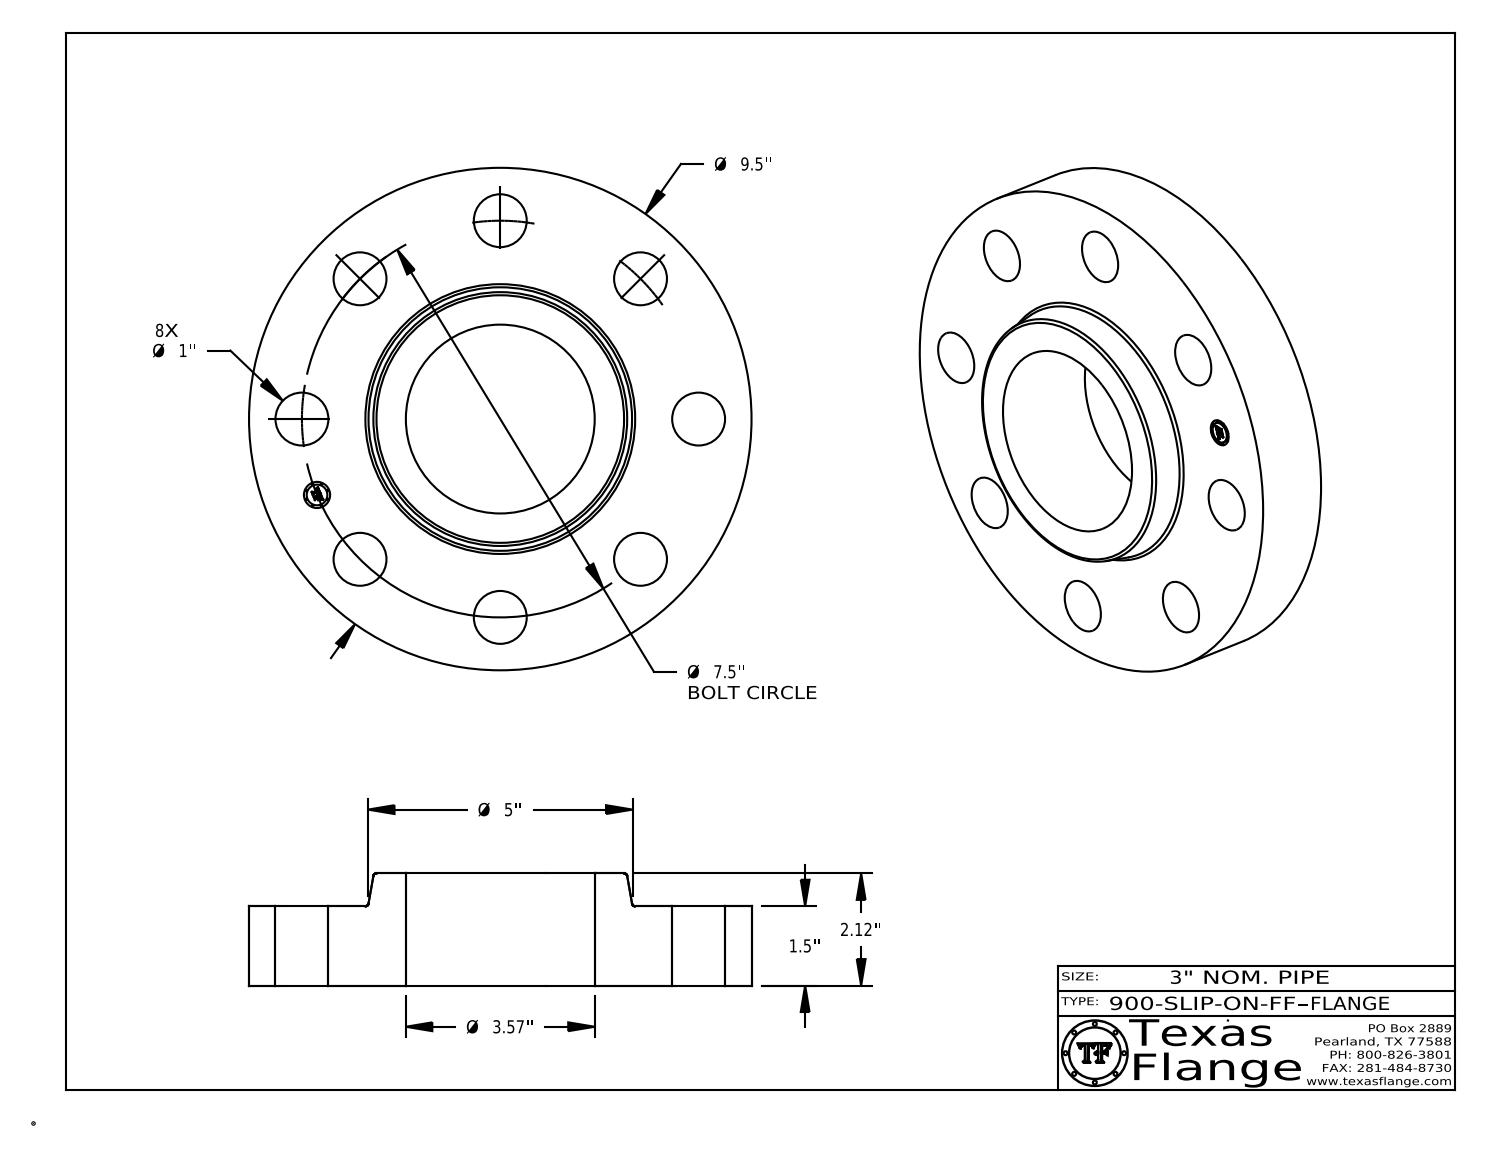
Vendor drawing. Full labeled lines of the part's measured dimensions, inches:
Part name (STEP PRODUCT): 900-SLIP-ON-FF
STEP written by: CATIA V5 STEP AP214 (AUTOMOTIVE_DESIGN)
Units: inches
Bodies: 1 solid, 414 faces (368 planar, 40 cylindrical, 6 other)
Overall size (bounding box): 9.5 × 9.5 × 2.12
Volume: 87.33 in³ · Surface area: 223 in²
Round holes (diameter × count): ⌀1 ×8, ⌀0.495 ×1, ⌀3.57 ×1
Round bosses / shafts (diameter × count): ⌀0.03 ×8, ⌀9.5 ×1, ⌀0.39 ×1
Main face-to-face distances: 1.5, 2.12, 0.62, 0.015, 1.485, 0.635, 0.148, 0.145, 0.027, 0.096
Hole centre spacings: 3.75, 2.87, 5.303, 6.929, 1.463, 6.236, 7.356, 7.5
